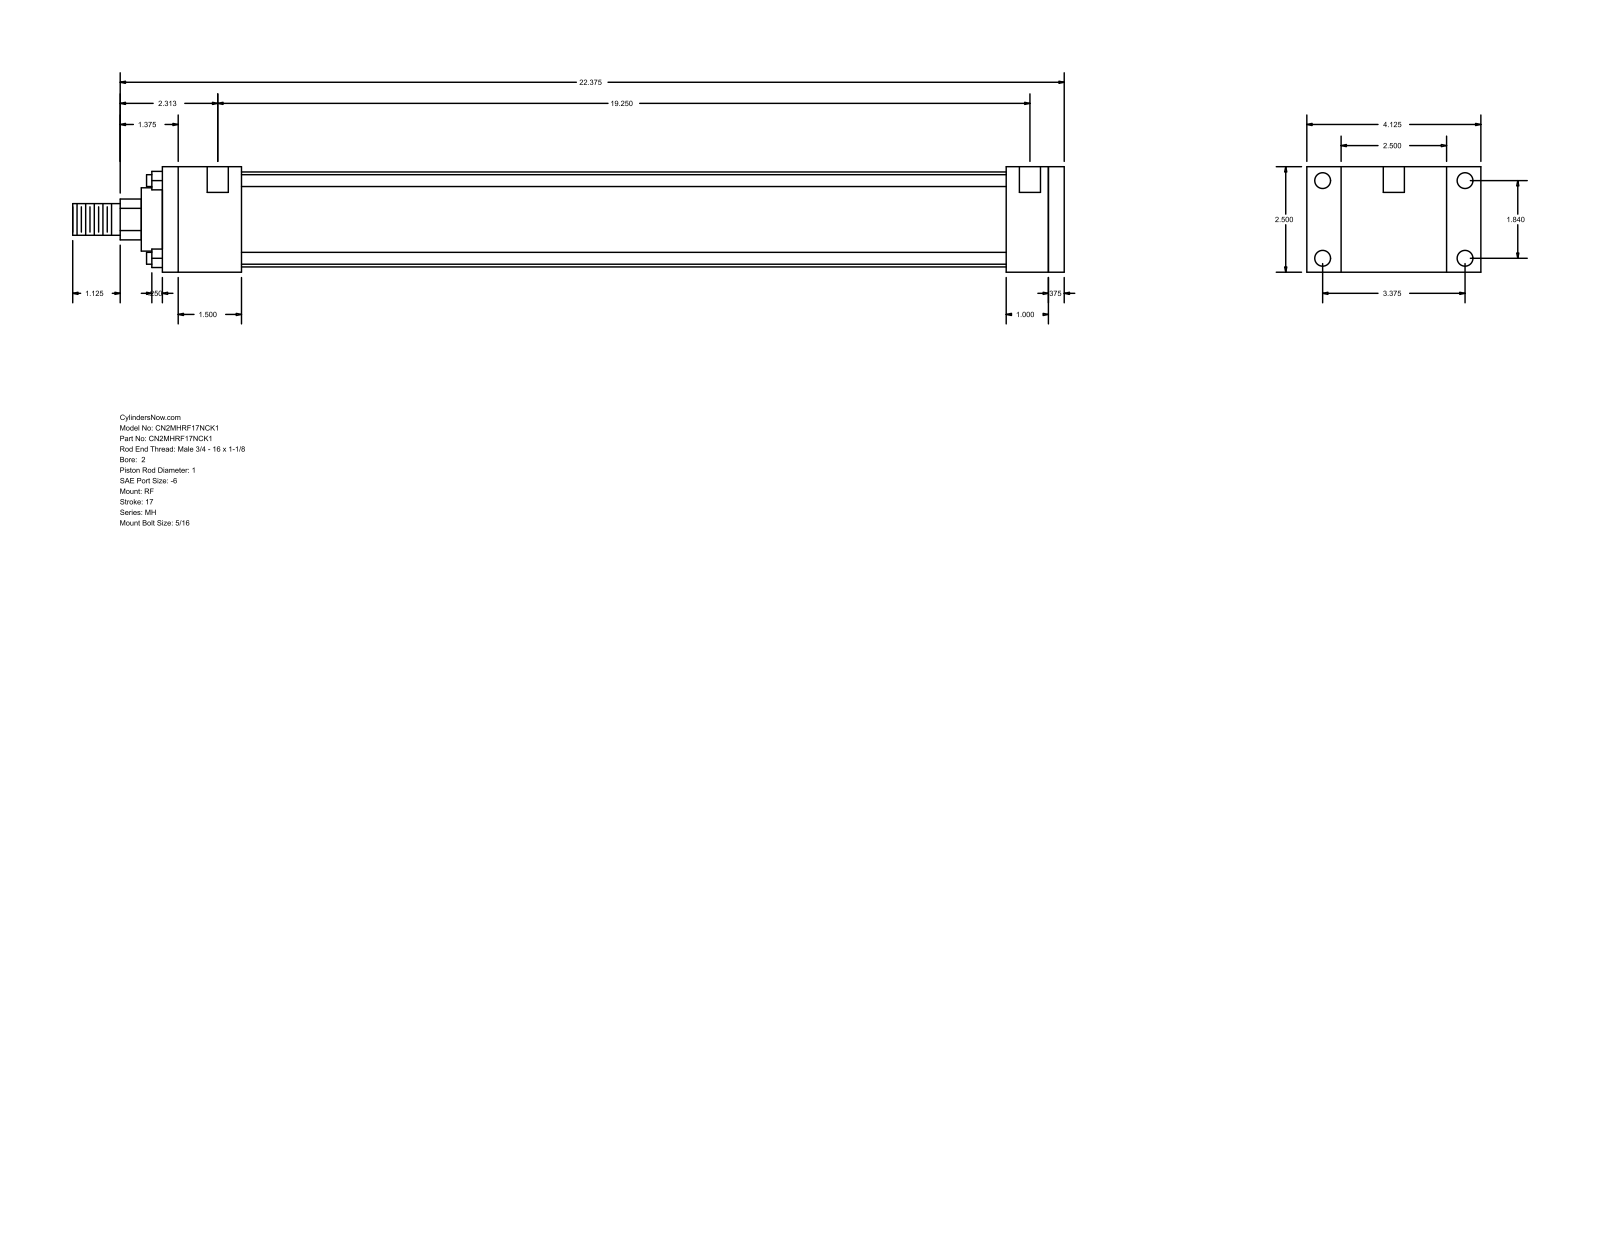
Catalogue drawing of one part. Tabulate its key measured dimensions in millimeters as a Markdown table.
| quantity | value |
| --- | --- |
| part name | MH_RF__0200_1 |
| STEP written by | GSSL Pune (CONFIG_CONTROL_DESIGN) |
| units | millimeters |
| bodies | 0 solids, 92 faces (64 planar, 28 cylindrical, 0 other) |
| overall size | 596.9 × 104.78 × 63.5 |
| round holes (diameter × count) | 5.56 × 4, 9.53 × 4, 12.7 × 2 |
| round bosses / shafts (diameter × count) | 7.14 × 4, 57.15 × 1, 38.1 × 1, 25.4 × 1, 19.05 × 1 |
| partial cylindrical surfaces (radius × count) | 12.29 × 1 |
| main face-to-face distances | 63.5, 542.93, 533.4, 9.53, 20.64, 25.4, 47.63, 508, 460.37, 485.77 |
| hole center spacings | 46.74, 85.72, 97.63, 496.88, 3.17, 4.76, 488.95, 492.12 |
